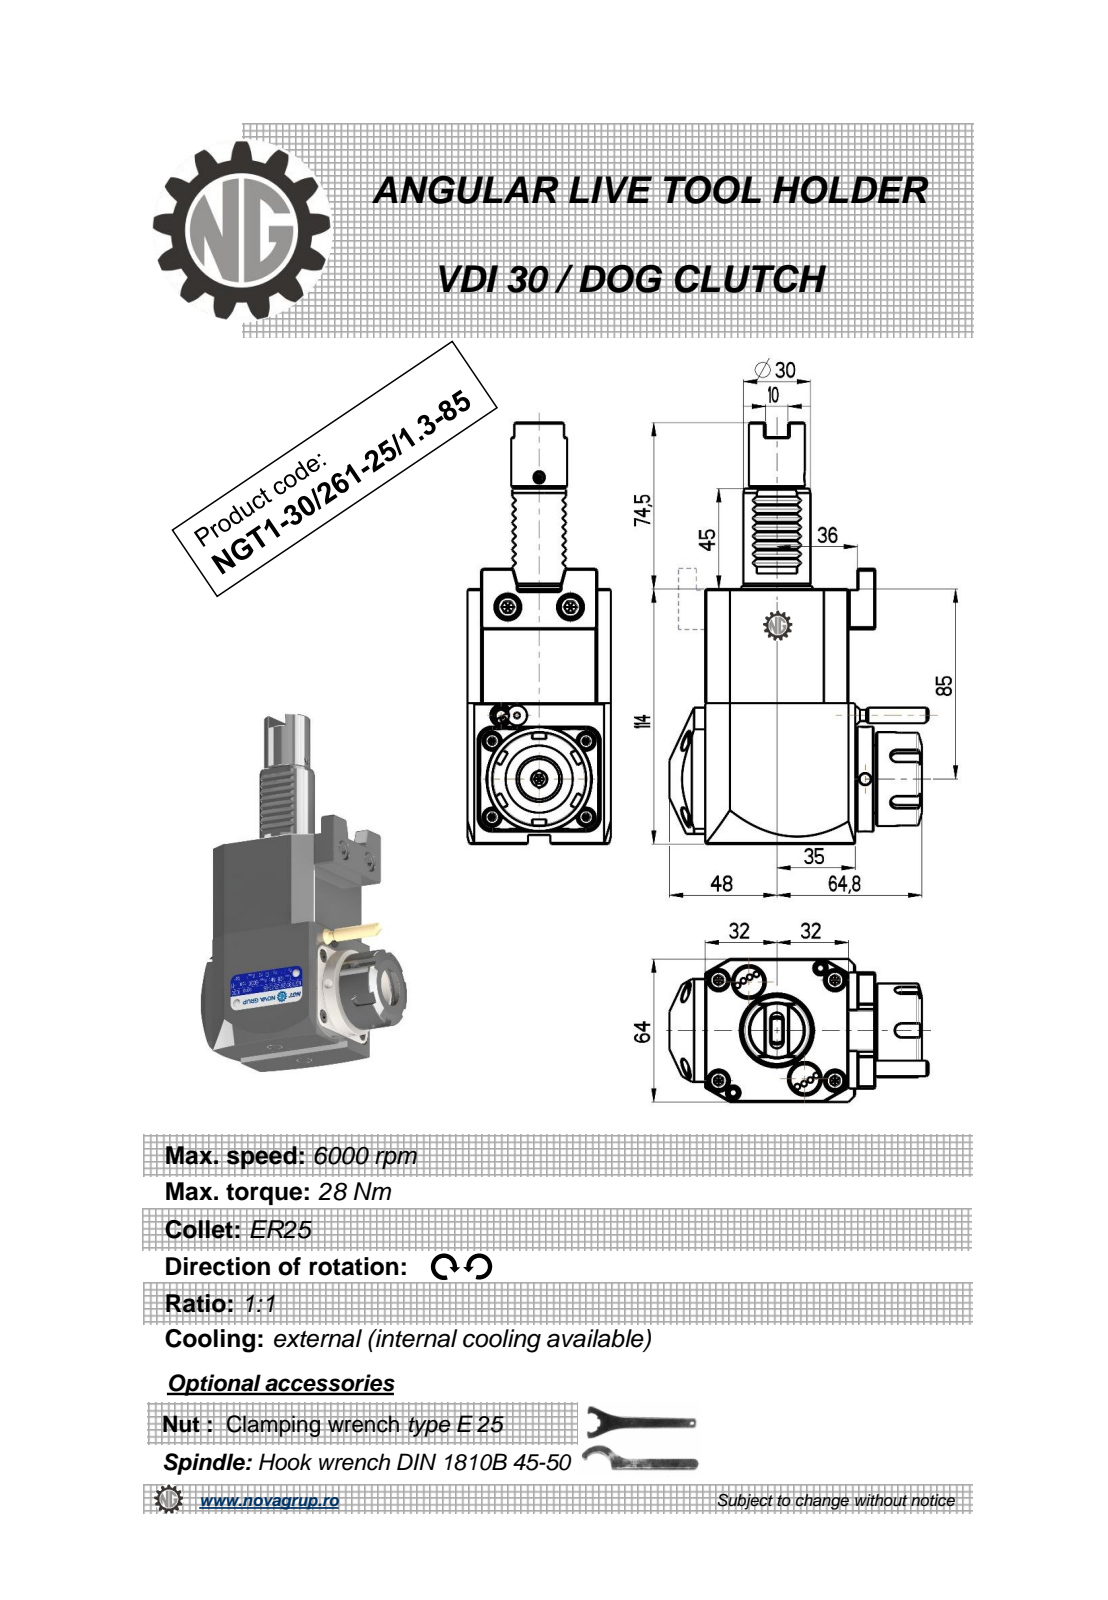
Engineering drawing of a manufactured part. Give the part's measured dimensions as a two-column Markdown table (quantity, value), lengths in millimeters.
| quantity | value |
| --- | --- |
| part name | NGT1_30_261_25_1_3_85 |
| STEP written by | PRO/ENGINEER BY PARAMETRIC TECHNOLOGY CORPORATION, 2010280 (CONFIG_CONTROL_DESIGN) |
| units | millimeters |
| bodies | 1 solid, 436 faces (229 planar, 75 cylindrical, 132 other) |
| overall size | 188.5 × 115.83 × 64 |
| volume | 583 987 mm³ |
| surface area | 56 100 mm² |
| round holes (diameter × count) | 5 × 2, 2.5 × 1, 3 × 1, 4.2 × 1, 20.3 × 1 |
| round bosses / shafts (diameter × count) | 47 × 1, 42 × 1, 35 × 1, 30 × 1, 25 × 1, 8.96 × 1, 7 × 1, 5 × 1 |
| partial cylindrical surfaces (radius × count) | 0.3 × 16, 0.26 × 6, 3 × 5, 3.5 × 4, 0.5 × 2, 1 × 2, 160 × 2, 8.9 × 1 |
| main face-to-face distances | 64, 114, 9, 3, 0.5, 67.2, 3.2, 76.42, 67, 0.8 |
| hole center spacings | 33.19, 107.85, 135 |
